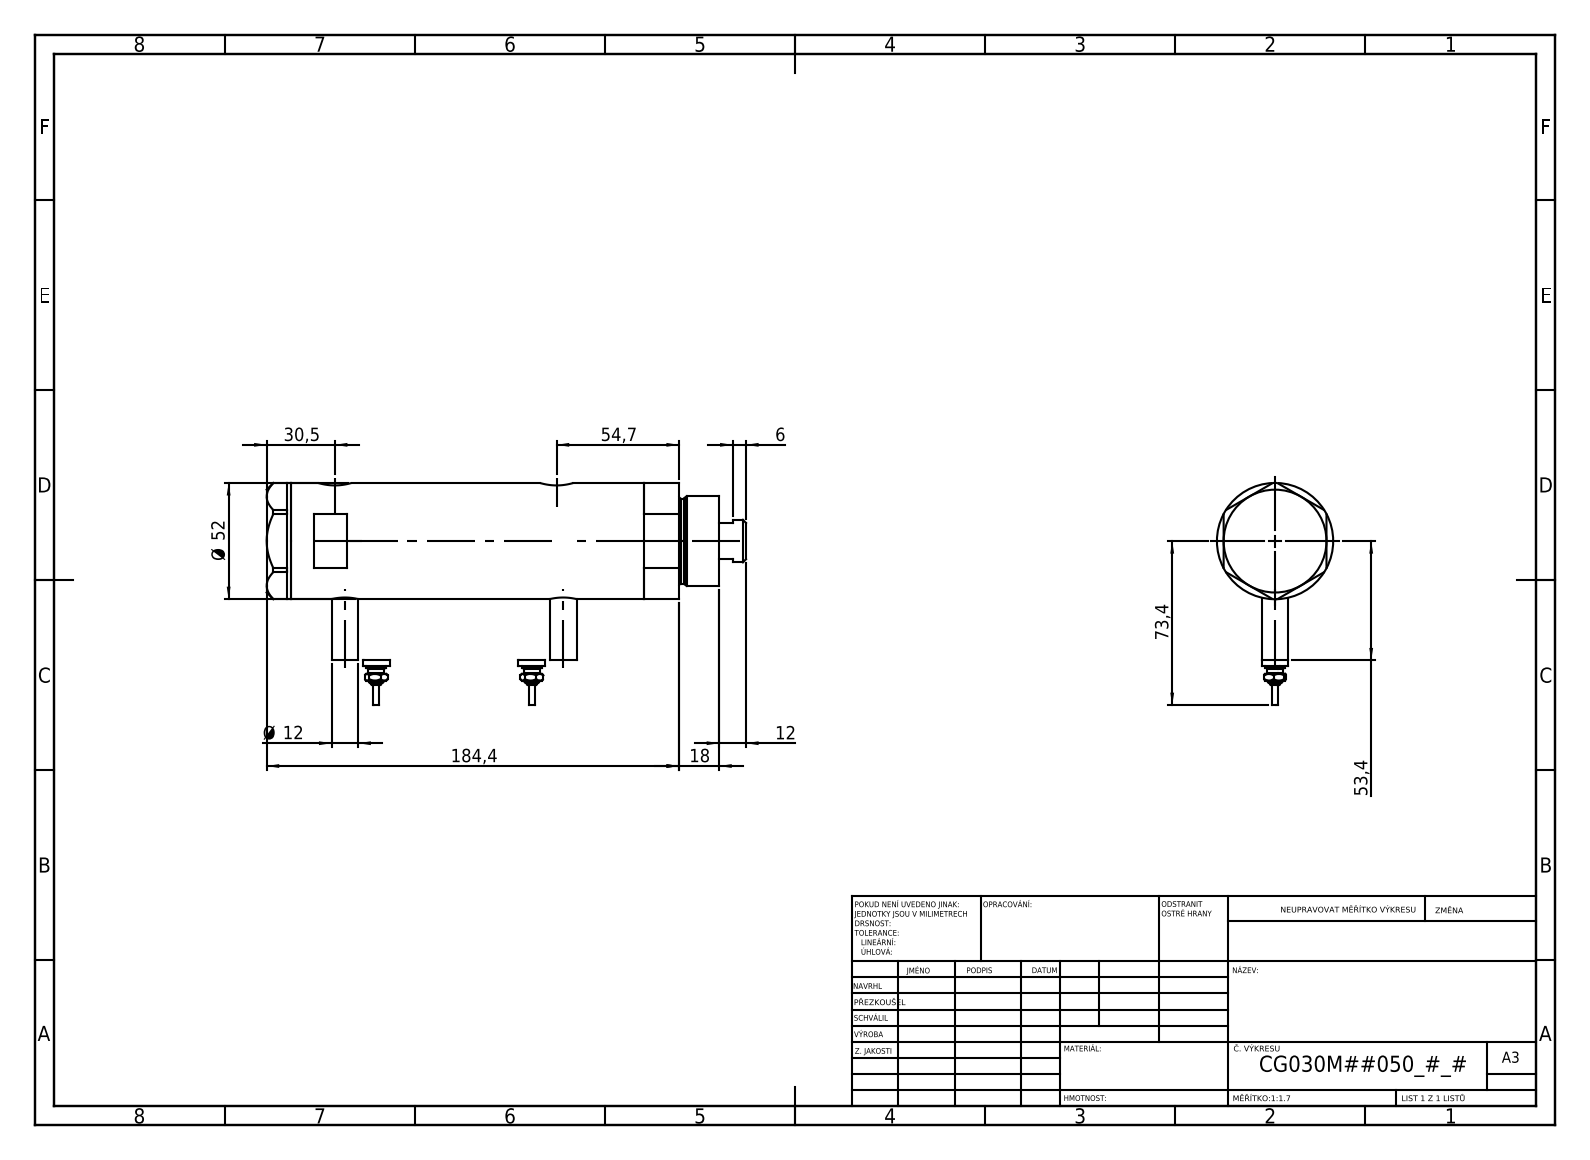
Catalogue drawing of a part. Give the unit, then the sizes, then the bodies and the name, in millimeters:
Units: millimetres
Overall size (bounding box): 214.4 × 99.4 × 52
Round holes (diameter × count): ⌀9.73 ×2, ⌀12.5 ×2, ⌀15 ×2, ⌀6.5 ×1, ⌀20 ×1, ⌀21.5 ×1, ⌀30 ×1, ⌀33 ×1, ⌀44 ×1
Round bosses / shafts (diameter × count): ⌀12 ×4, ⌀9 ×2, ⌀7 ×2, ⌀4.5 ×2, ⌀2.5 ×2, ⌀52 ×1, ⌀40 ×1, ⌀38 ×1
Main face-to-face distances: 121.5, 23.8, 97.7, 11, 34.8, 132.5, 46, 36.4, 168.9, 157.9
Hole centre spacings: 2.9, 4.5, 94.7, 97.6, 99.2, 102.1
Volume: 396 792 mm³ · Surface area: 89 841 mm²
Bodies: 6 solids, 226 faces (93 planar, 69 cylindrical, 64 other)
Part name (STEP PRODUCT): V270CG_MIDDLE; V270CG_BACK; Switch; V270CG_FRONT (+1 more)
STEP written by: SolidWorks 2019 (CONFIG_CONTROL_DESIGN)
